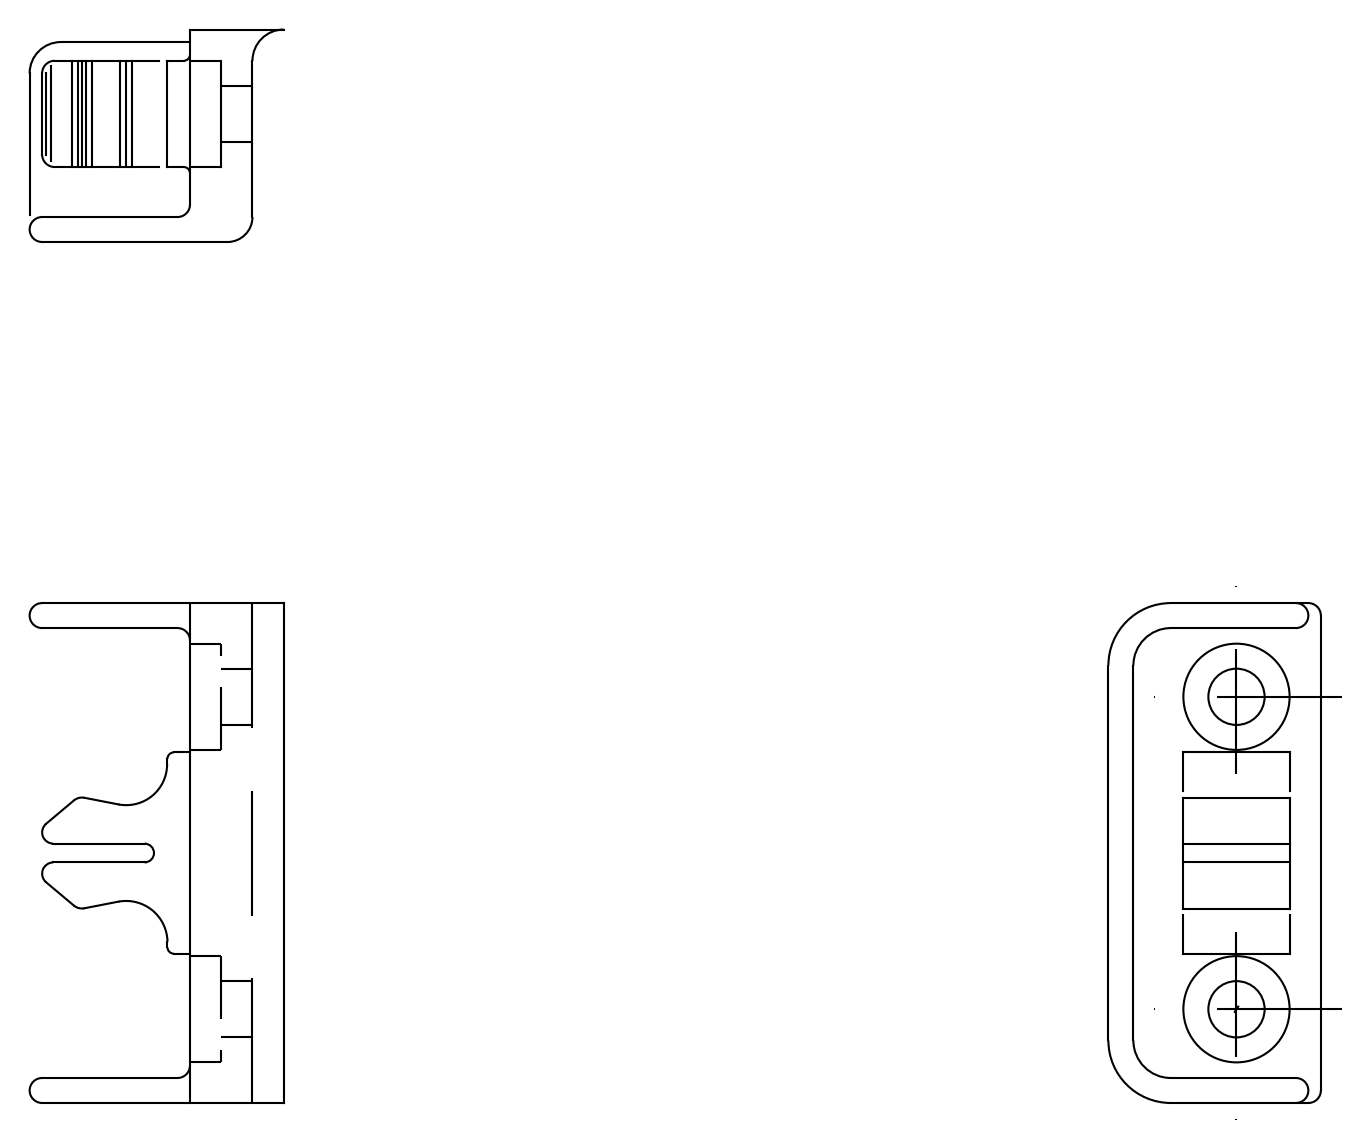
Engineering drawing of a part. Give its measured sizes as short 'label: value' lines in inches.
written by: THINKDESIGN (CONFIG_CONTROL_DESIGN)
unit: in
bodies: 1 solid, 62 faces (24 planar, 30 cylindrical, 8 other)
size: 1.575 × 0.787 × 0.669
volume: 0.326 in³; area: 6.941 in²
holes: 2× ⌀0.167, 2× ⌀0.335, 1× ⌀0.138
rounds: 8× R0.039, 3× R0.02, 3× R0.079, 2× R0.394
face distances: 0.098, 0.079, 0.669, 0.571, 0.748, 1.496, 0.138, 1.575, 0.157, 0.827
hole spacings: 0.984
